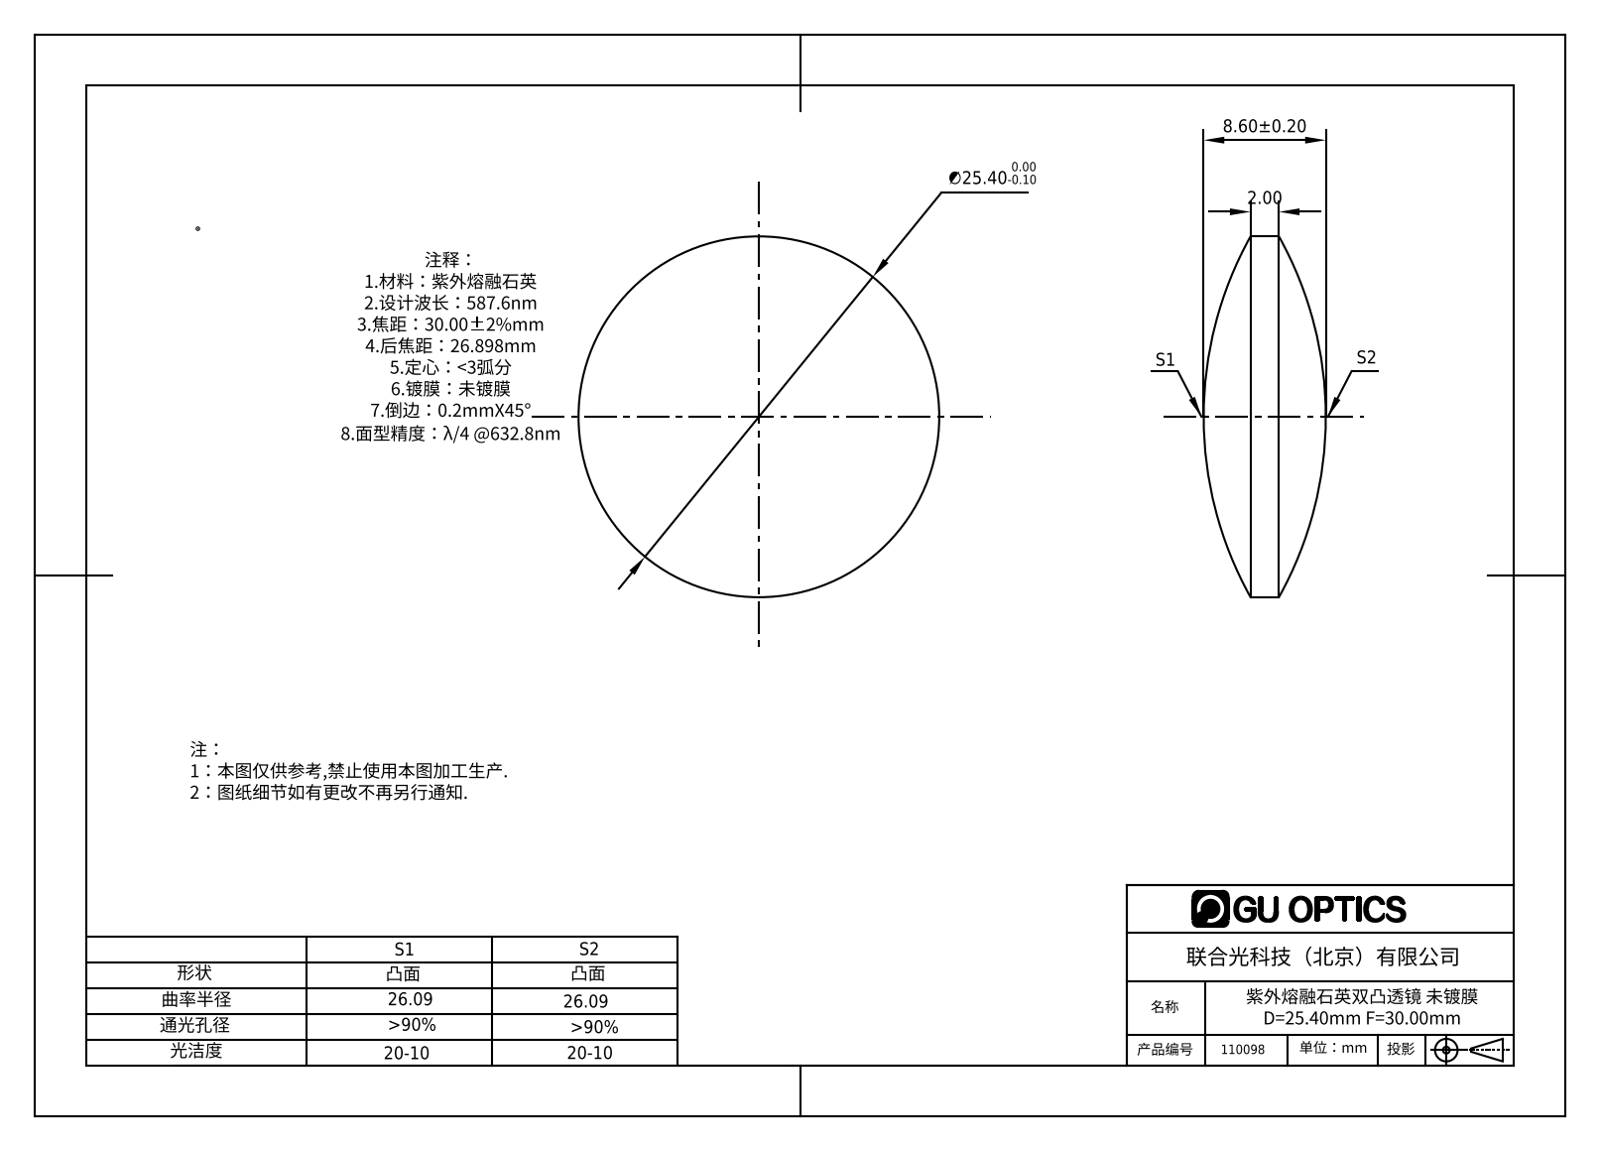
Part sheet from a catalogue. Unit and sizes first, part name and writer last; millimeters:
Units: millimetres
Overall size (bounding box): 25.4 × 25.4 × 8.6
Round bosses / shafts (diameter × count): ⌀25.4 ×1
Volume: 2 723 mm³ · Surface area: 1 241 mm²
Bodies: 1 solid, 6 faces (0 planar, 2 cylindrical, 4 other)
Part name (STEP PRODUCT): 110098
STEP written by: SolidWorks 2016 (CONFIG_CONTROL_DESIGN)
